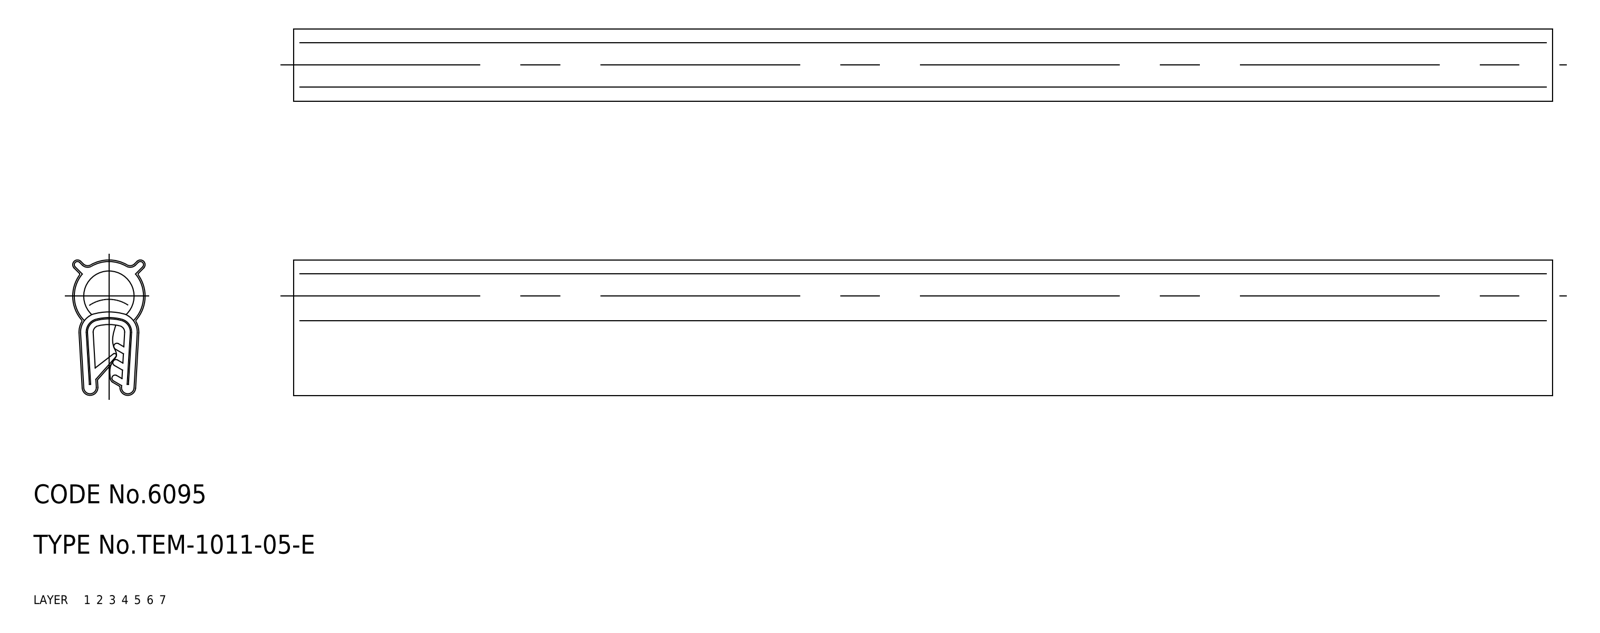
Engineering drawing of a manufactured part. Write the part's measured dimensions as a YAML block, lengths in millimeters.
part_name: "sheet; rubber foam; gasket; center core (+1 more)"
step_written_by: "CADfix (AUTOMOTIVE_DESIGN)"
units: millimeters
bodies: {solids: 4, faces: 131, planar: 0, cylindrical: 0, other: 131}
overall_size: [200, 21.5, 11.5]
volume: 24573
surface_area: 78497
